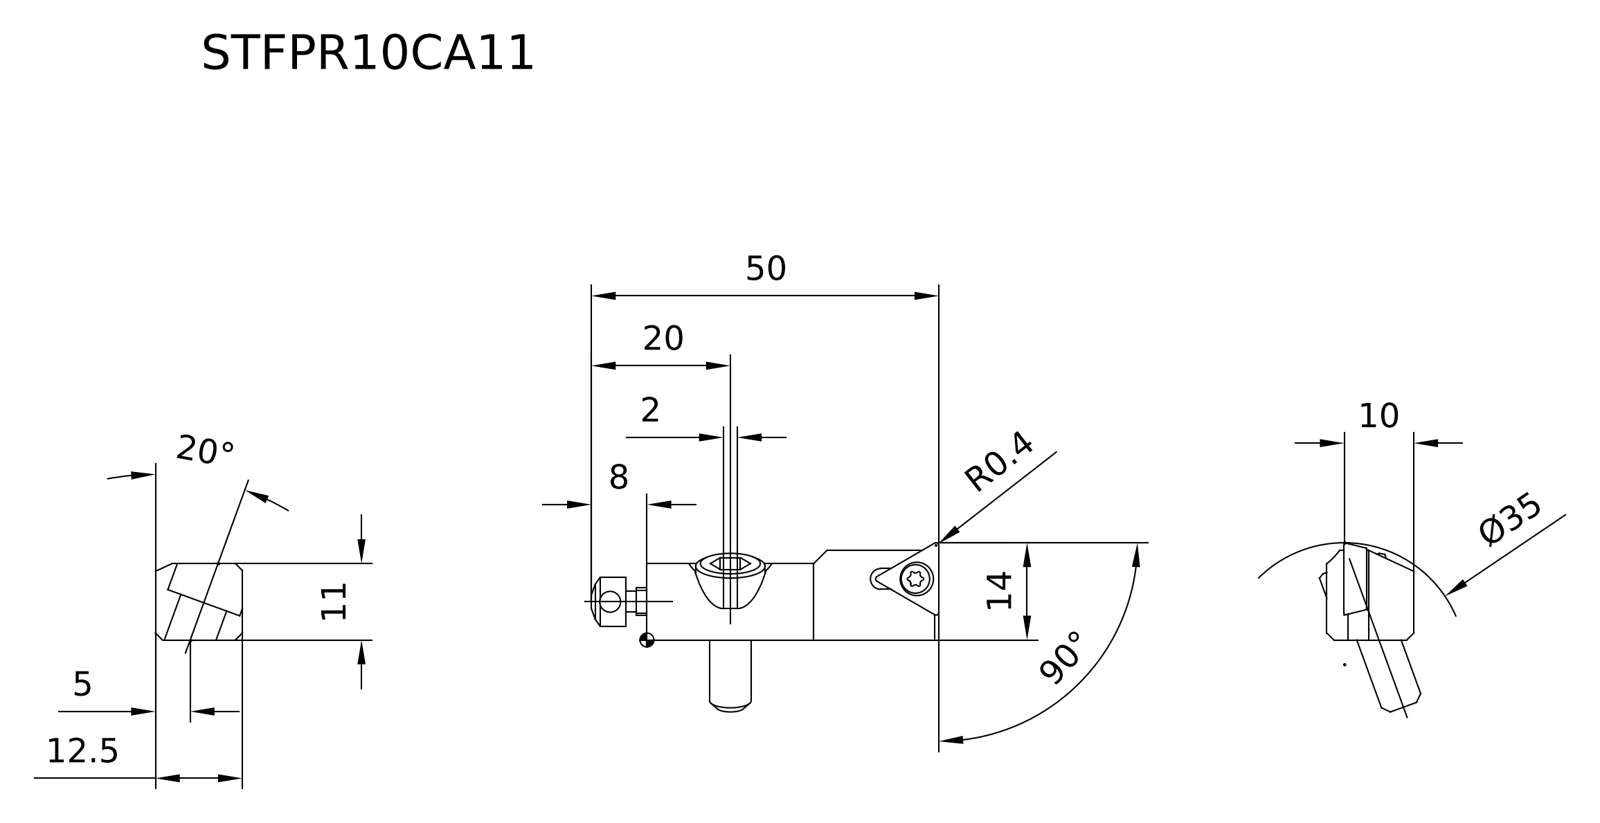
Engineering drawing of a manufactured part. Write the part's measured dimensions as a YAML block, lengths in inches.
part_name: "STFPR10CA11_ASM"
step_written_by: "SIEMENS PLM Software NX 10.0 (AUTOMOTIVE_DESIGN)"
units: inches
bodies: {solids: 5, faces: 142, planar: 50, cylindrical: 60, other: 32}
overall_size: [1.943, 0.917, 0.573]
volume: 0.306
surface_area: 5.65
round_holes:
  - {diameter: 0.071, count: 2}
  - {diameter: 0.098, count: 1}
  - {diameter: 0.13, count: 1}
  - {diameter: 0.165, count: 1}
round_bosses_or_shafts:
  - {diameter: 0.118, count: 2}
  - {diameter: 0.394, count: 1}
  - {diameter: 0.276, count: 1}
  - {diameter: 0.236, count: 1}
  - {diameter: 0.197, count: 1}
  - {diameter: 0.161, count: 1}
  - {diameter: 0.157, count: 1}
partial_cylinders:
  - {radius: 0.009, count: 6}
  - {radius: 0.01, count: 6}
  - {radius: 0.019, count: 6}
  - {radius: 0.022, count: 6}
  - {radius: 0.138, count: 2}
  - {radius: 0.217, count: 2}
  - {radius: 0.059, count: 1}
  - {radius: 0.394, count: 1}
face_to_face_distances: [0.492, 0.433, 0.118, 0.236, 0.076, 0.509, 0.106, 0.197, 0.598, 0.039]
hole_center_spacings: [1.547]
